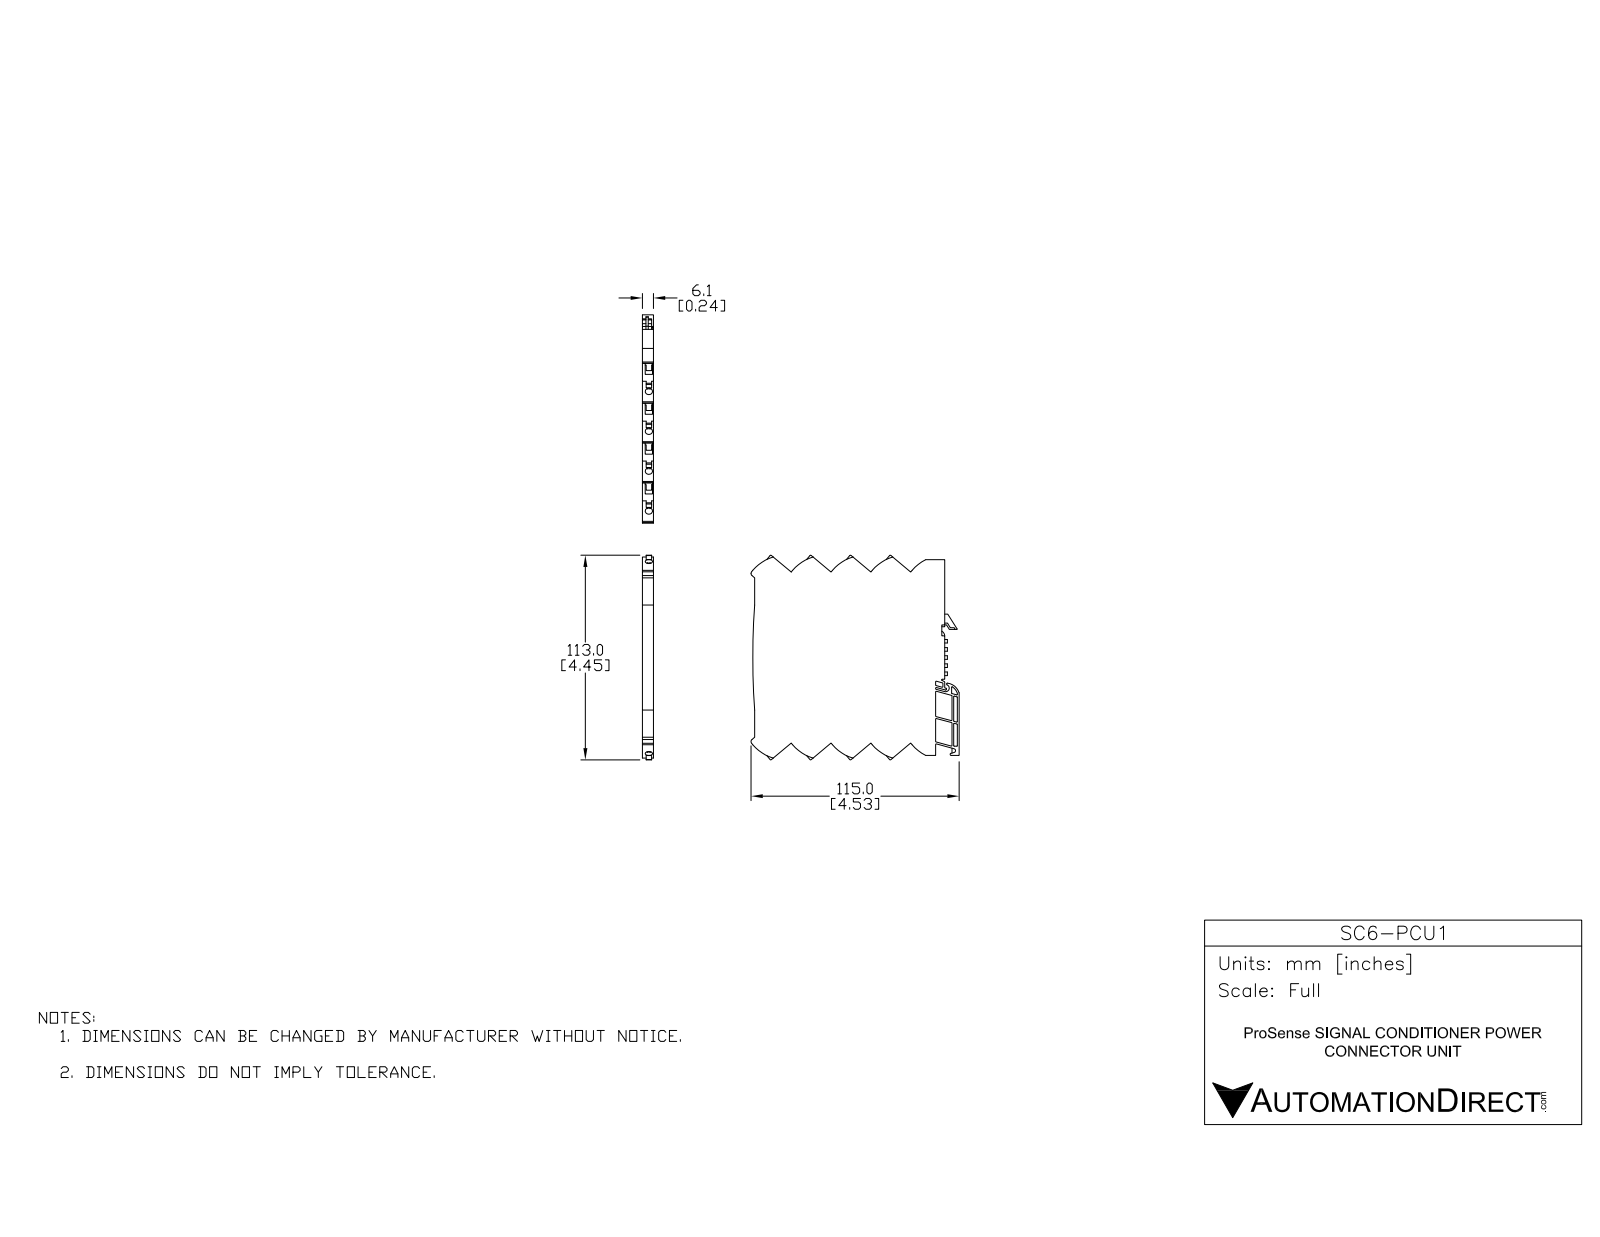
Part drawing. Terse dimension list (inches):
name: SC6-PCU1
written by: SolidWorks 2017 (AUTOMOTIVE_DESIGN)
unit: in
bodies: 1 solid, 455 faces (338 planar, 117 cylindrical, 0 other)
size: 4.528 × 4.448 × 0.24
volume: 3.977 in³; area: 43.6 in²
holes: 8× ⌀0.157
rounds: 33× R0.012, 10× R0.02, 10× R0.059, 10× R0.918, 2× R0.008, 1× R0.022, 1× R0.043, 1× R0.058
face distances: 0.24, 0.039, 0.118, 0.157, 0.081, 0.557, 0.159, 0.041, 0.138, 0.199
hole spacings: 0.557, 1.113, 0.557, 1.67
